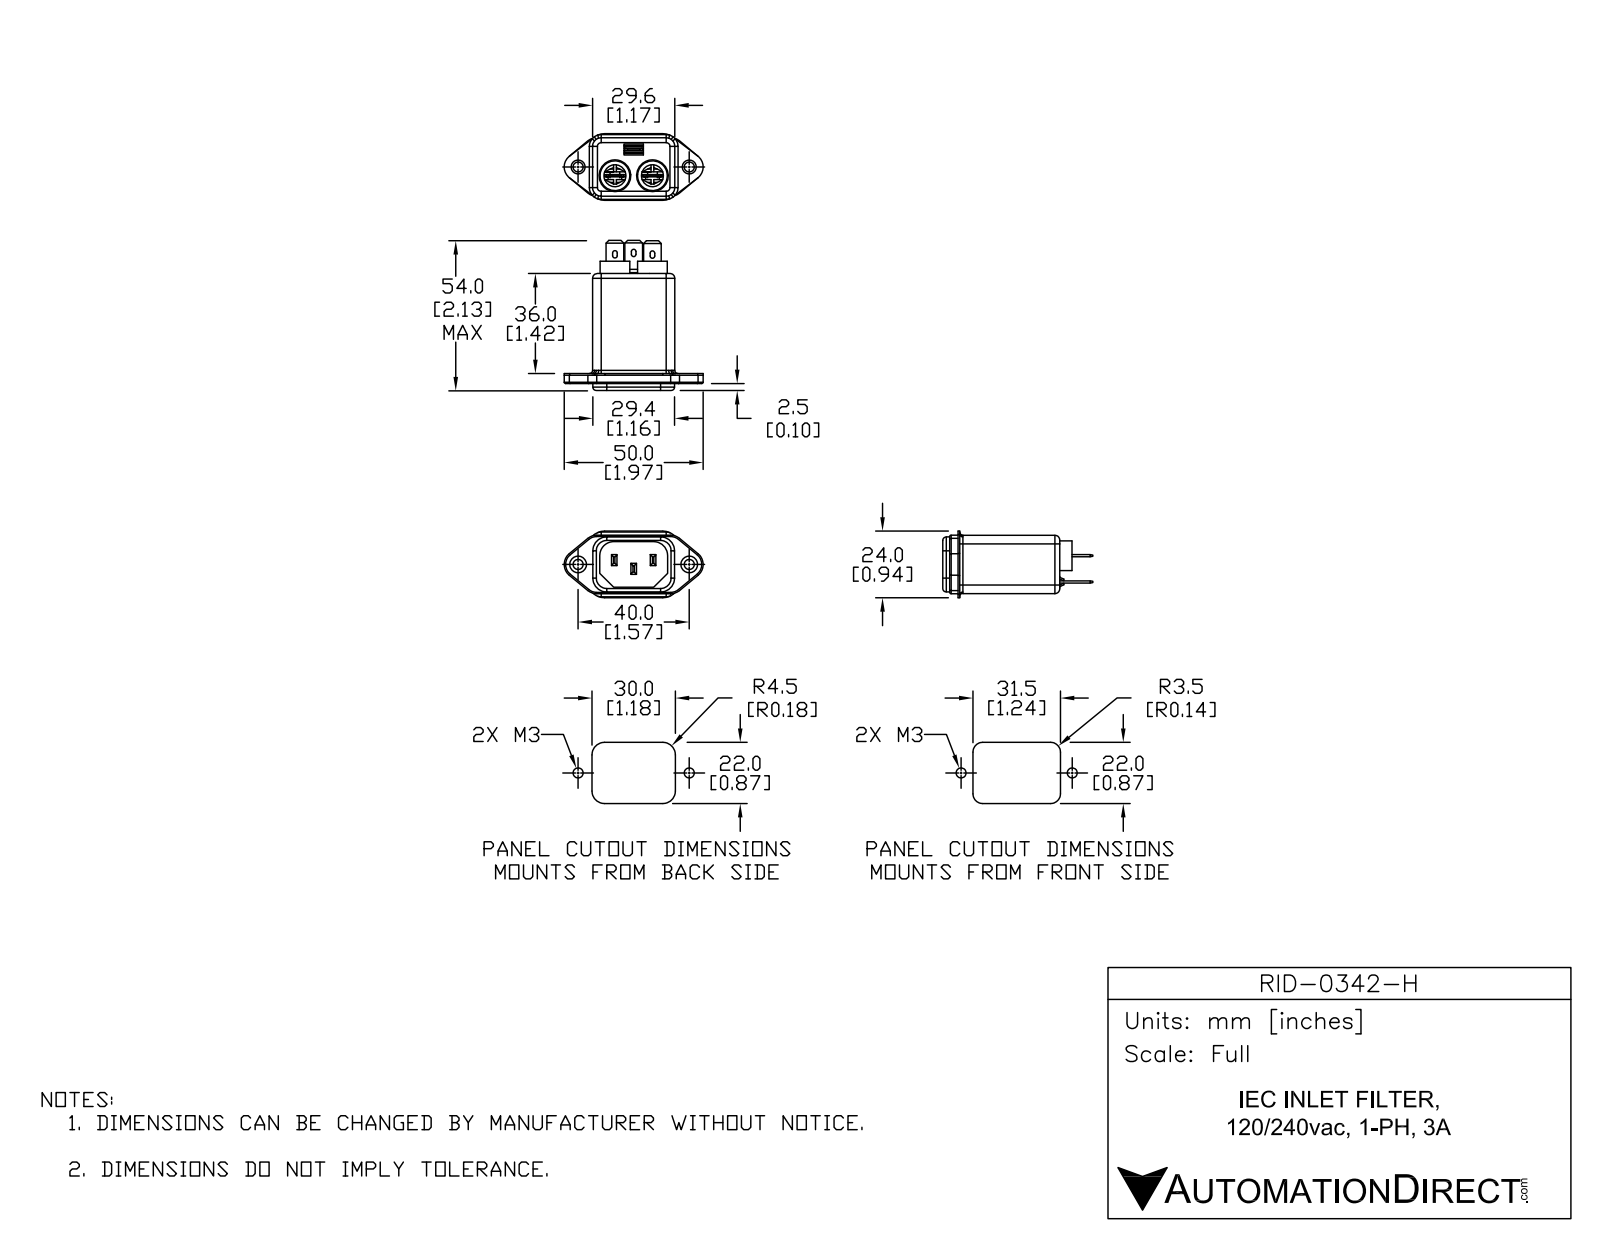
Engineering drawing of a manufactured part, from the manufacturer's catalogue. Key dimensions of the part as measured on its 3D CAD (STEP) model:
Part name (STEP PRODUCT): inlet body DAC-3; ENCLOSURE A1_+; RID-0342-H
STEP written by: SolidWorks 2015 (AUTOMOTIVE_DESIGN)
Units: millimetres
Bodies: 11 solids, 591 faces (410 planar, 142 cylindrical, 39 other)
Overall size (bounding box): 54 × 50 × 24
Volume: 12 008 mm³ · Surface area: 20 049 mm²
Round holes (diameter × count): ⌀1.5 ×2, ⌀1.65 ×2, ⌀3.6 ×2, ⌀5 ×2, ⌀7.9 ×2, ⌀11.4 ×2, ⌀1.75 ×1
Round bosses / shafts (diameter × count): ⌀10.7 ×2
Partial cylindrical surfaces — rounded edges, fillets, slot ends (radius × count): R5 ×12, R0.3 ×11, R0.5 ×8, R1 ×8, R0.8 ×7, R1.25 ×6, R2.5 ×6, R1.75 ×4
Main face-to-face distances: 0.6, 20.4, 21, 19.8, 29, 1.05, 28.9, 36, 1.45, 11.2
Hole centre spacings: 13.5, 13.62, 26.93, 6.77, 6.78, 10.47, 10.77, 11.21
